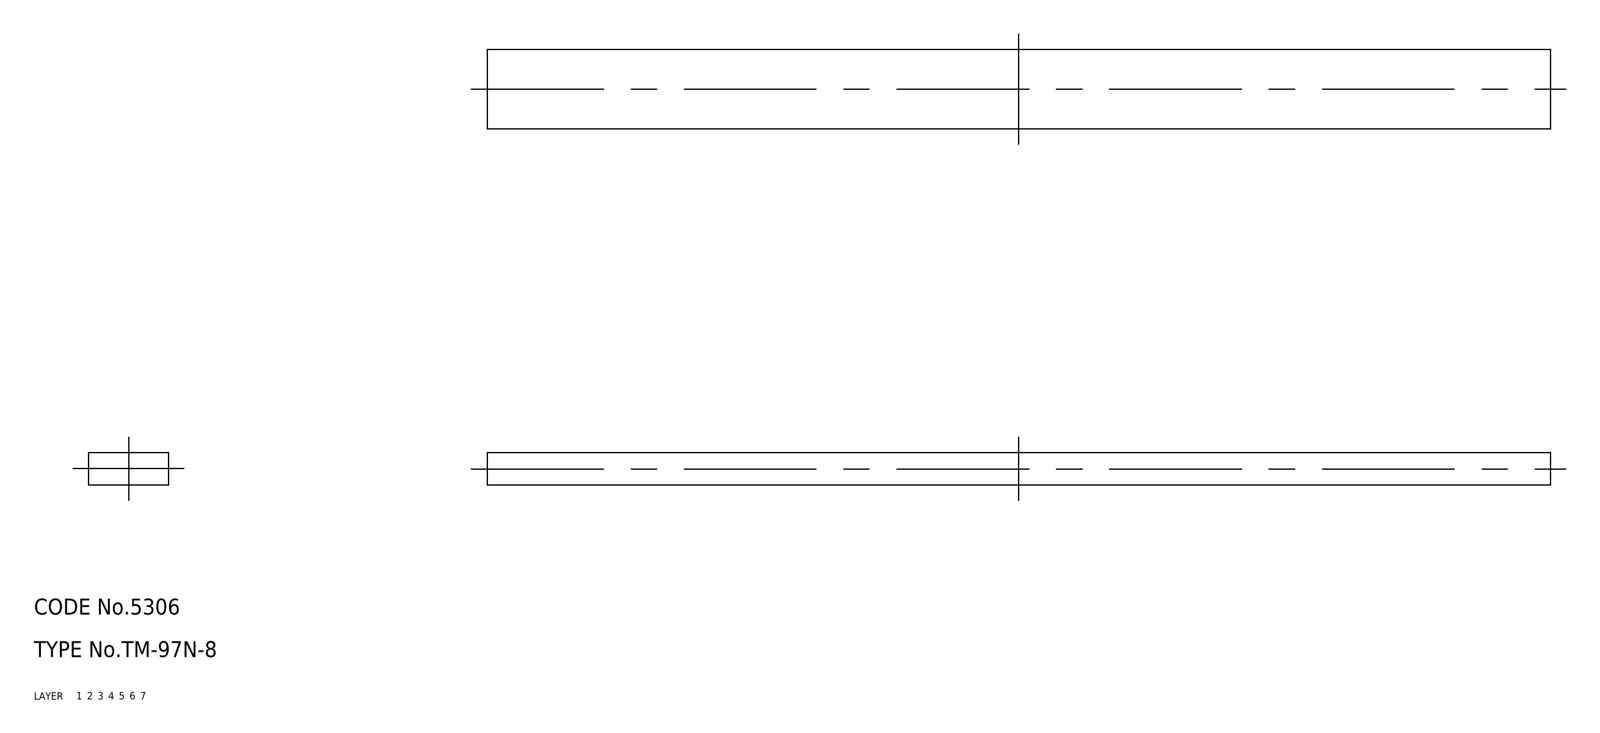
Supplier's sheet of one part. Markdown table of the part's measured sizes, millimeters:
| quantity | value |
| --- | --- |
| part name | 67109034 |
| STEP written by | CADfix (AUTOMOTIVE_DESIGN) |
| units | millimeters |
| bodies | 1 solid, 6 faces (0 planar, 0 cylindrical, 6 other) |
| overall size | 200 × 15 × 6 |
| volume | 18 000 mm³ |
| surface area | 8 580 mm² |
